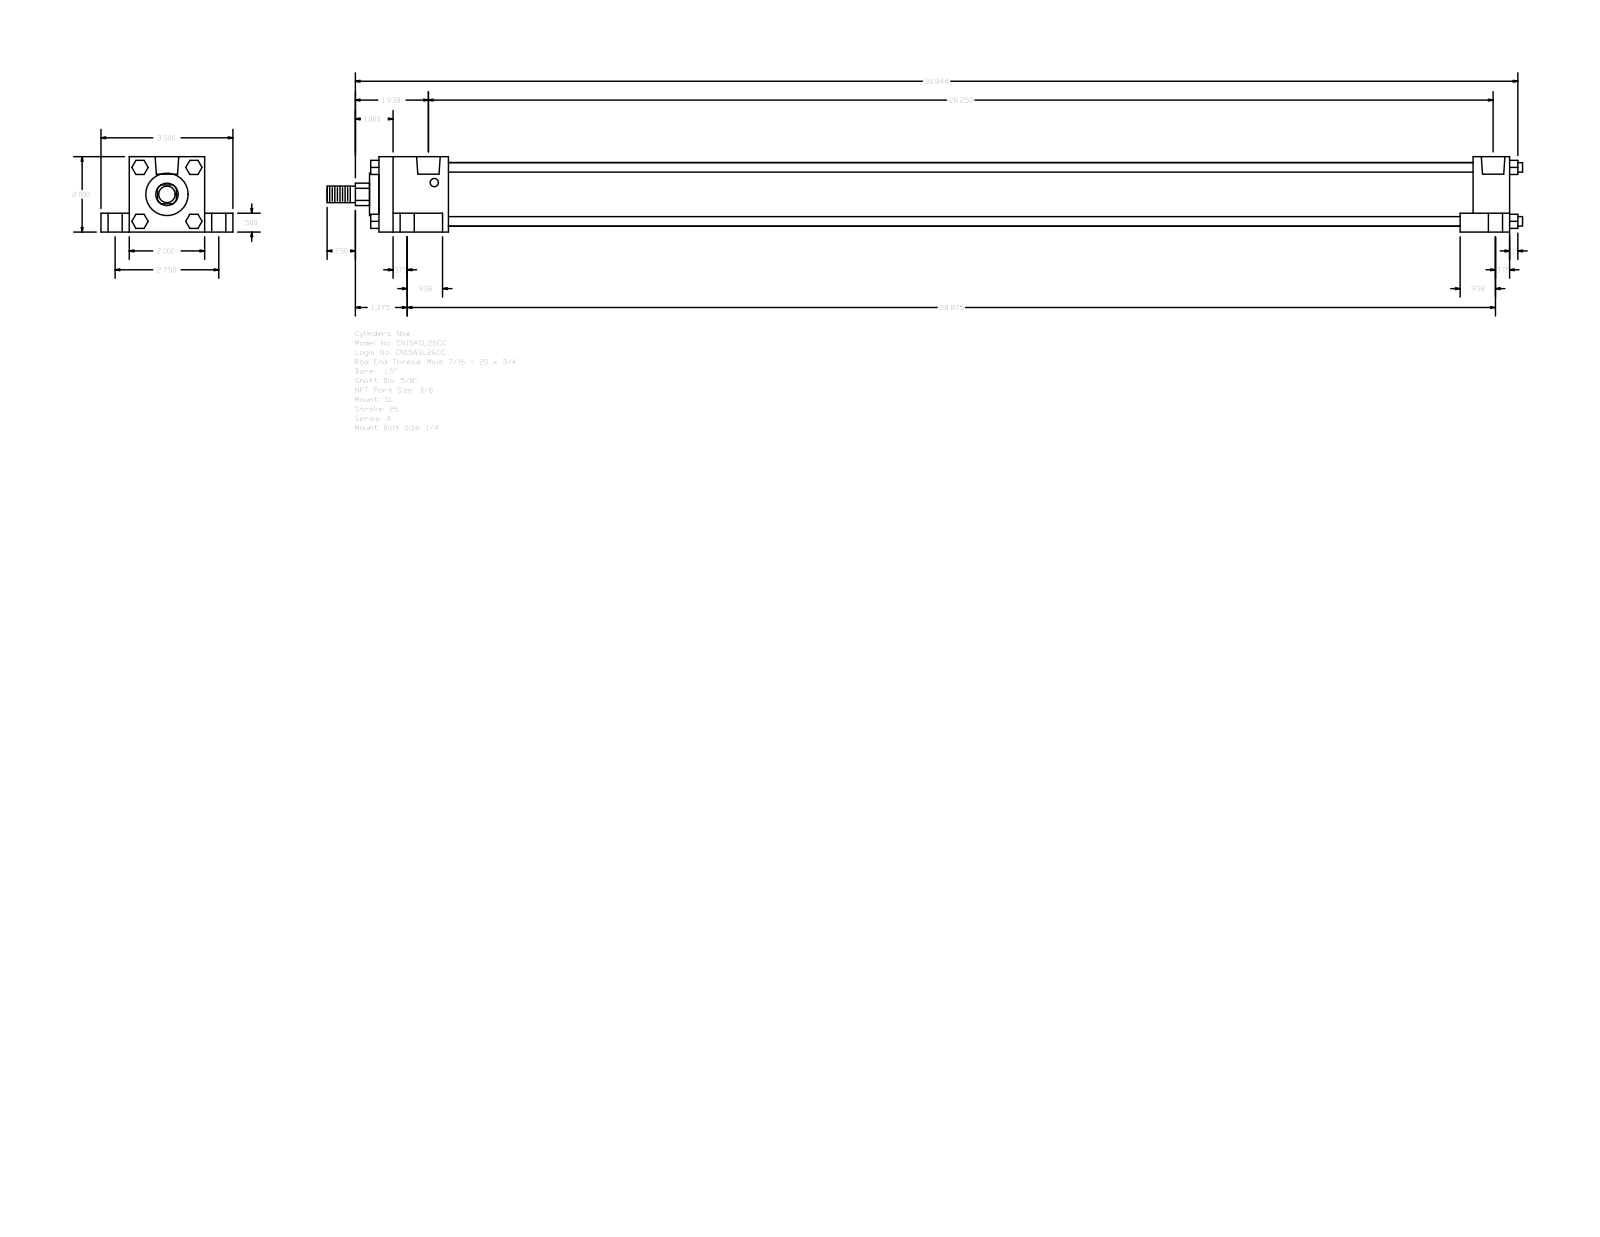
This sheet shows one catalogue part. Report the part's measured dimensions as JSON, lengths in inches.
{"part_name": "A_SL__0150_0.625", "step_written_by": "GSSL Pune (CONFIG_CONTROL_DESIGN)", "units": "inches", "bodies": {"solids": 0, "faces": 148, "planar": 112, "cylindrical": 36, "other": 0}, "overall_size": [31.719, 3.5, 2], "round_holes": [[0.219, 4], [0.375, 4], [0.625, 4], [0.627, 2]], "round_bosses_or_shafts": [[0.25, 4], [1.69, 1], [1.125, 1], [0.625, 1], [0.437, 1]], "partial_cylinders_radius": [[0.297, 1]], "face_to_face_distances": [2, 0.75, 1.5, 0.5, 2.75, 30, 0.375, 1.313, 29.031, 0.969], "hole_center_spacings": [0.156, 1.376, 1.392, 1.485, 1.552, 2.75, 27.937, 28.094]}
